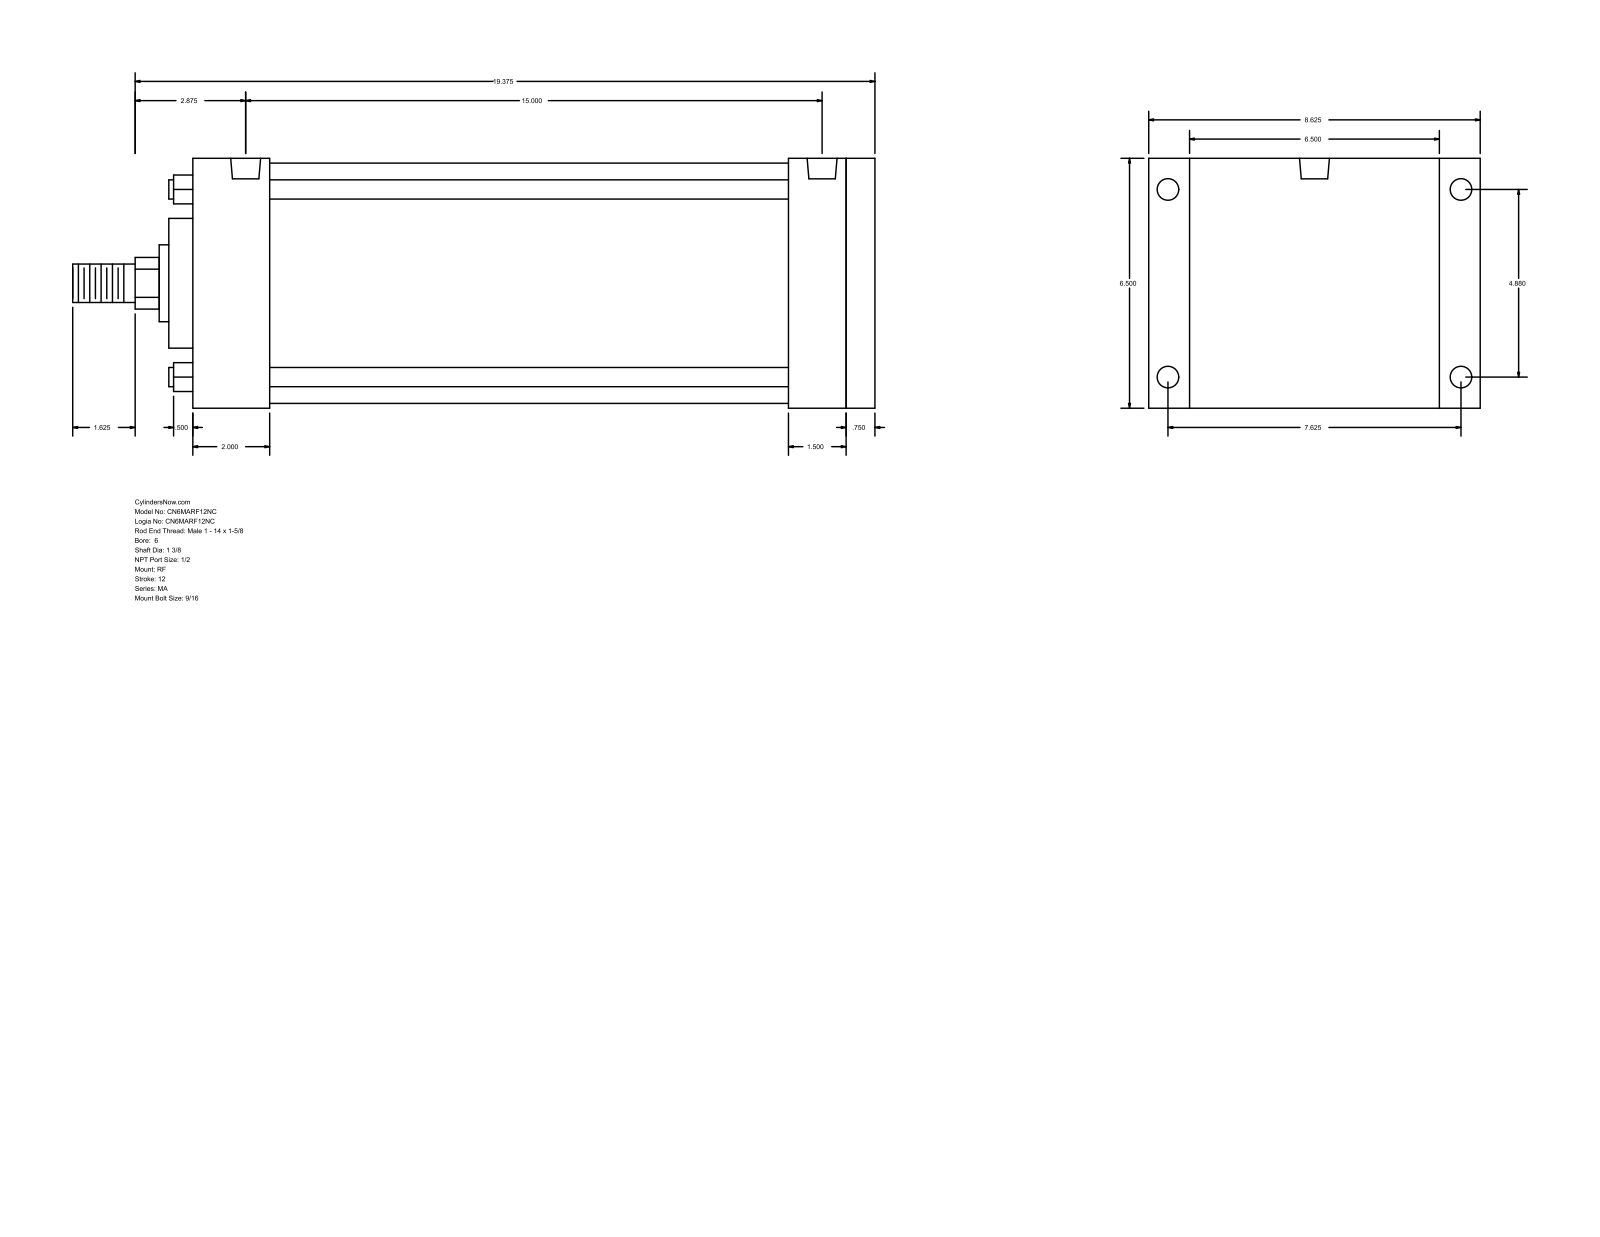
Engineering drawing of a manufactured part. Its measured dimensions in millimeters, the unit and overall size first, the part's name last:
Units: millimetres
Overall size (bounding box): 533.4 × 219.07 × 165.1
Round holes (diameter × count): ⌀14.29 ×4, ⌀17.46 ×4, ⌀19.77 ×2
Round bosses / shafts (diameter × count): ⌀12.7 ×4, ⌀158.75 ×1, ⌀85.72 ×1, ⌀50.8 ×1, ⌀34.92 ×1, ⌀25.4 ×1
Partial cylindrical surfaces — rounded edges, fillets, slot ends (radius × count): R17.06 ×1
Main face-to-face distances: 165.1, 454.02, 19.05, 434.97, 50.8, 384.17, 403.22, 396.88, 346.08, 38.09
Hole centre spacings: 123.96, 193.68, 229.95, 384.17, 3.18, 380.99
Bodies: 0 solids, 94 faces (65 planar, 29 cylindrical, 0 other)
Part name (STEP PRODUCT): MA_RF__0600_1.375
STEP written by: GSSL Pune (CONFIG_CONTROL_DESIGN)
